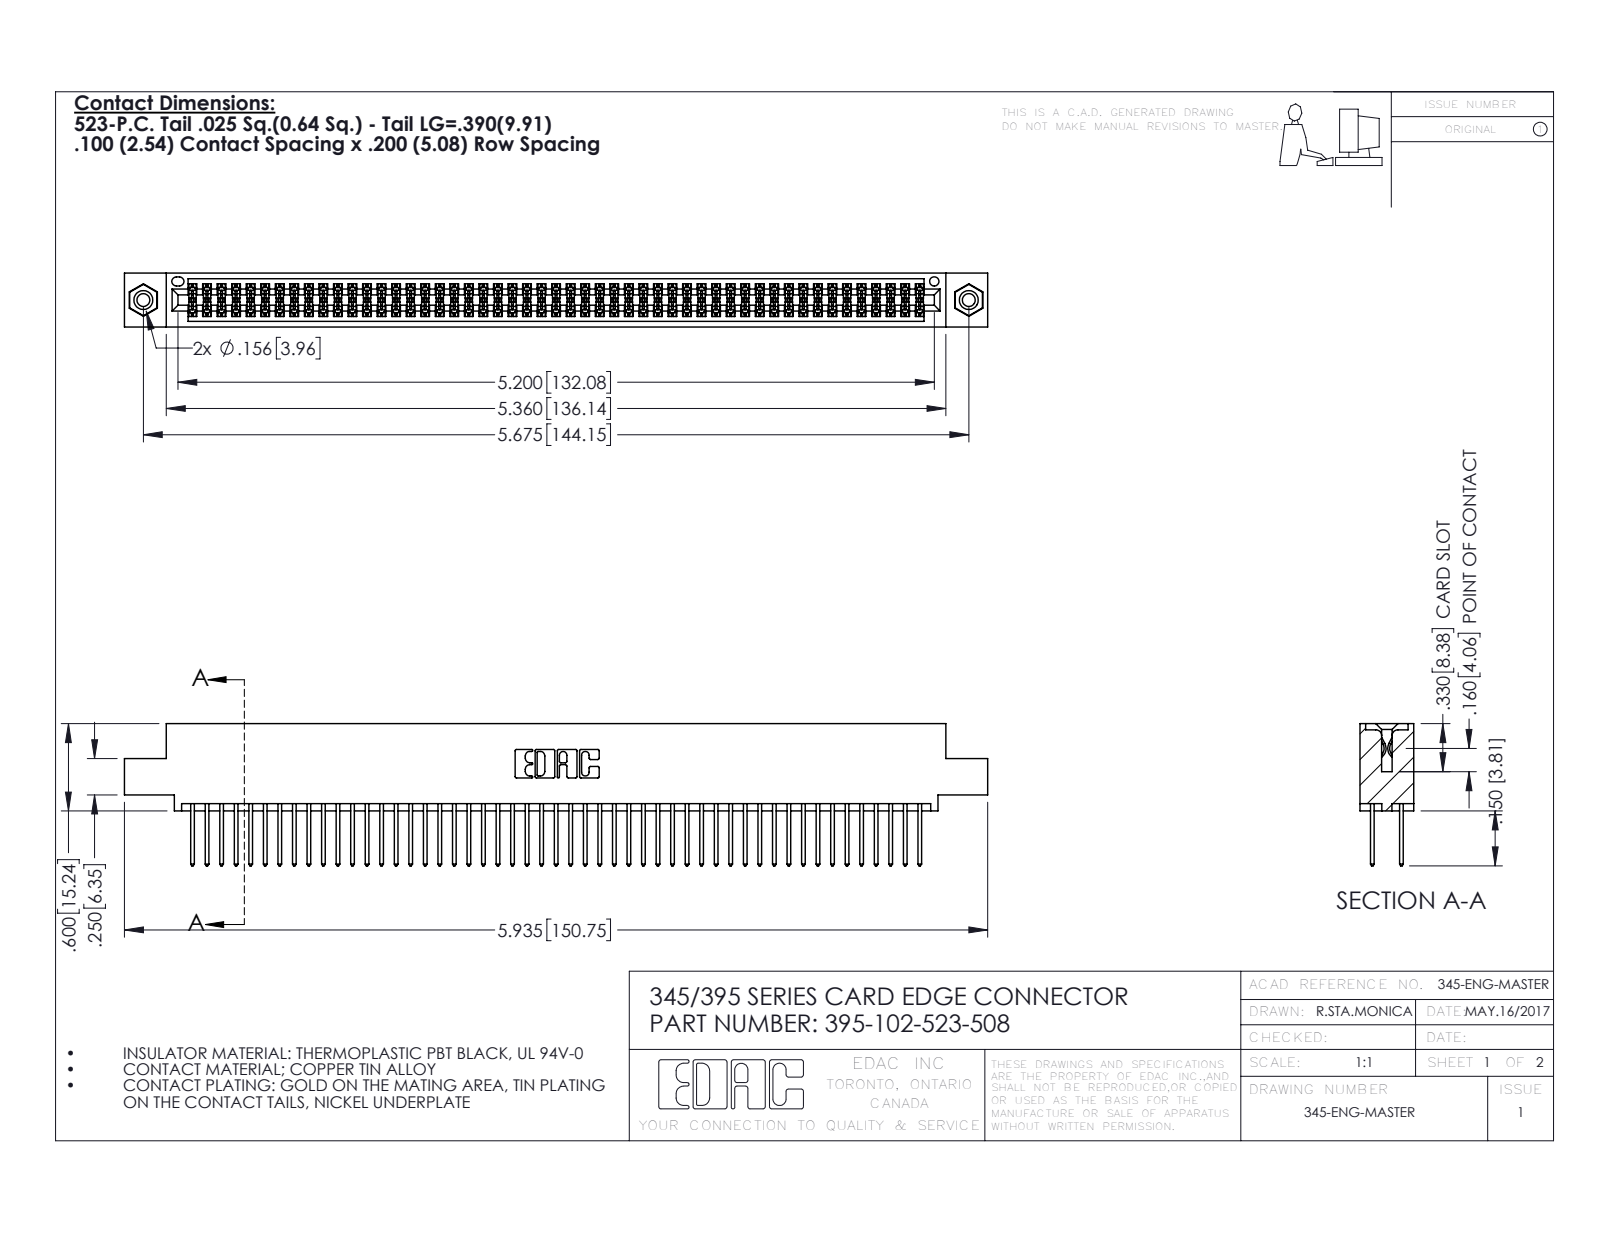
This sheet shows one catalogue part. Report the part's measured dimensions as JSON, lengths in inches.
{"part_name": "345 Part_0.110 Offset - 0.156 Dia-TI; 345-250-001_345-250-003-102; 395-102-523-508; 345-292-001_345-293-123", "step_written_by": "SolidWorks 2016 (CONFIG_CONTROL_DESIGN)", "units": "inches", "bodies": {"solids": 105, "faces": 5290, "planar": 3482, "cylindrical": 1792, "other": 16}, "overall_size": [5.935, 0.977, 0.37], "volume_in3": 0.907, "surface_area_in2": 35.93, "round_holes": [[0.089, 2], [0.125, 2], [0.156, 2], [0.064, 1]], "round_bosses_or_shafts": [[0.155, 2]], "partial_cylinders_radius": [[0.006, 153], [0.01, 102], [0.01, 22], [0.007, 6], [0.031, 6], [0.026, 3], [0.014, 2], [0.019, 2]], "face_to_face_distances": [0.072, 0.298, 0.2, 0.098, 0.272, 0.025, 0.37, 0.225, 0.175, 0.149], "hole_center_spacings": [0.27, 5.439, 5.675]}
